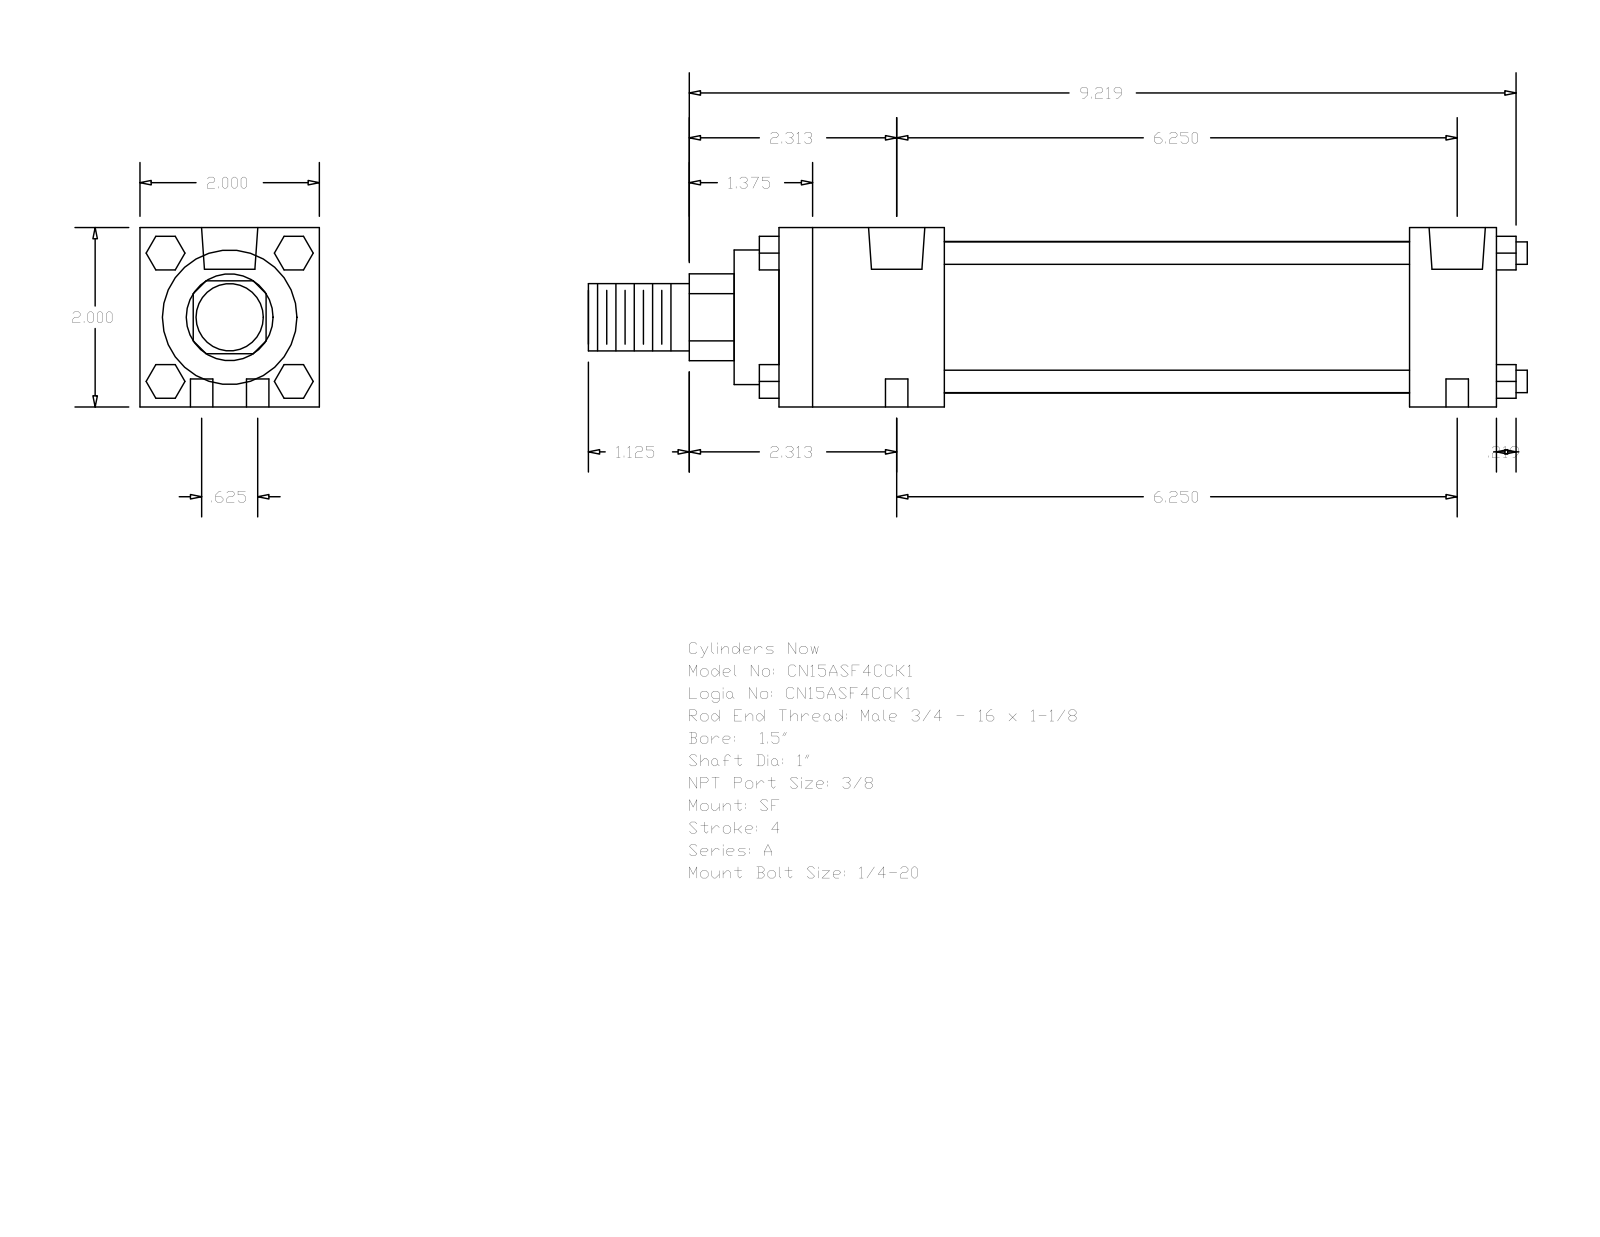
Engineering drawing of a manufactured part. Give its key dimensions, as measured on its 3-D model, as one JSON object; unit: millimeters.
{"part_name": "A_SF__0150_1", "step_written_by": "GSSL Pune (CONFIG_CONTROL_DESIGN)", "units": "millimeters", "bodies": {"solids": 0, "faces": 124, "planar": 94, "cylindrical": 30, "other": 0}, "overall_size": [265.91, 50.8, 50.8], "round_holes": [[6.35, 4], [5.56, 2], [15.93, 2]], "round_bosses_or_shafts": [[6.35, 4], [42.93, 1], [38.1, 1], [25.4, 1], [19.05, 1]], "partial_cylinders_radius": [[12.29, 1]], "face_to_face_distances": [50.8, 203.2, 46.83, 178.59, 131.76, 156.37, 24.61, 12.7, 59.53, 191.29], "hole_center_spacings": [7.94, 158.95, 158.75, 15.88, 159.54, 150.81]}
